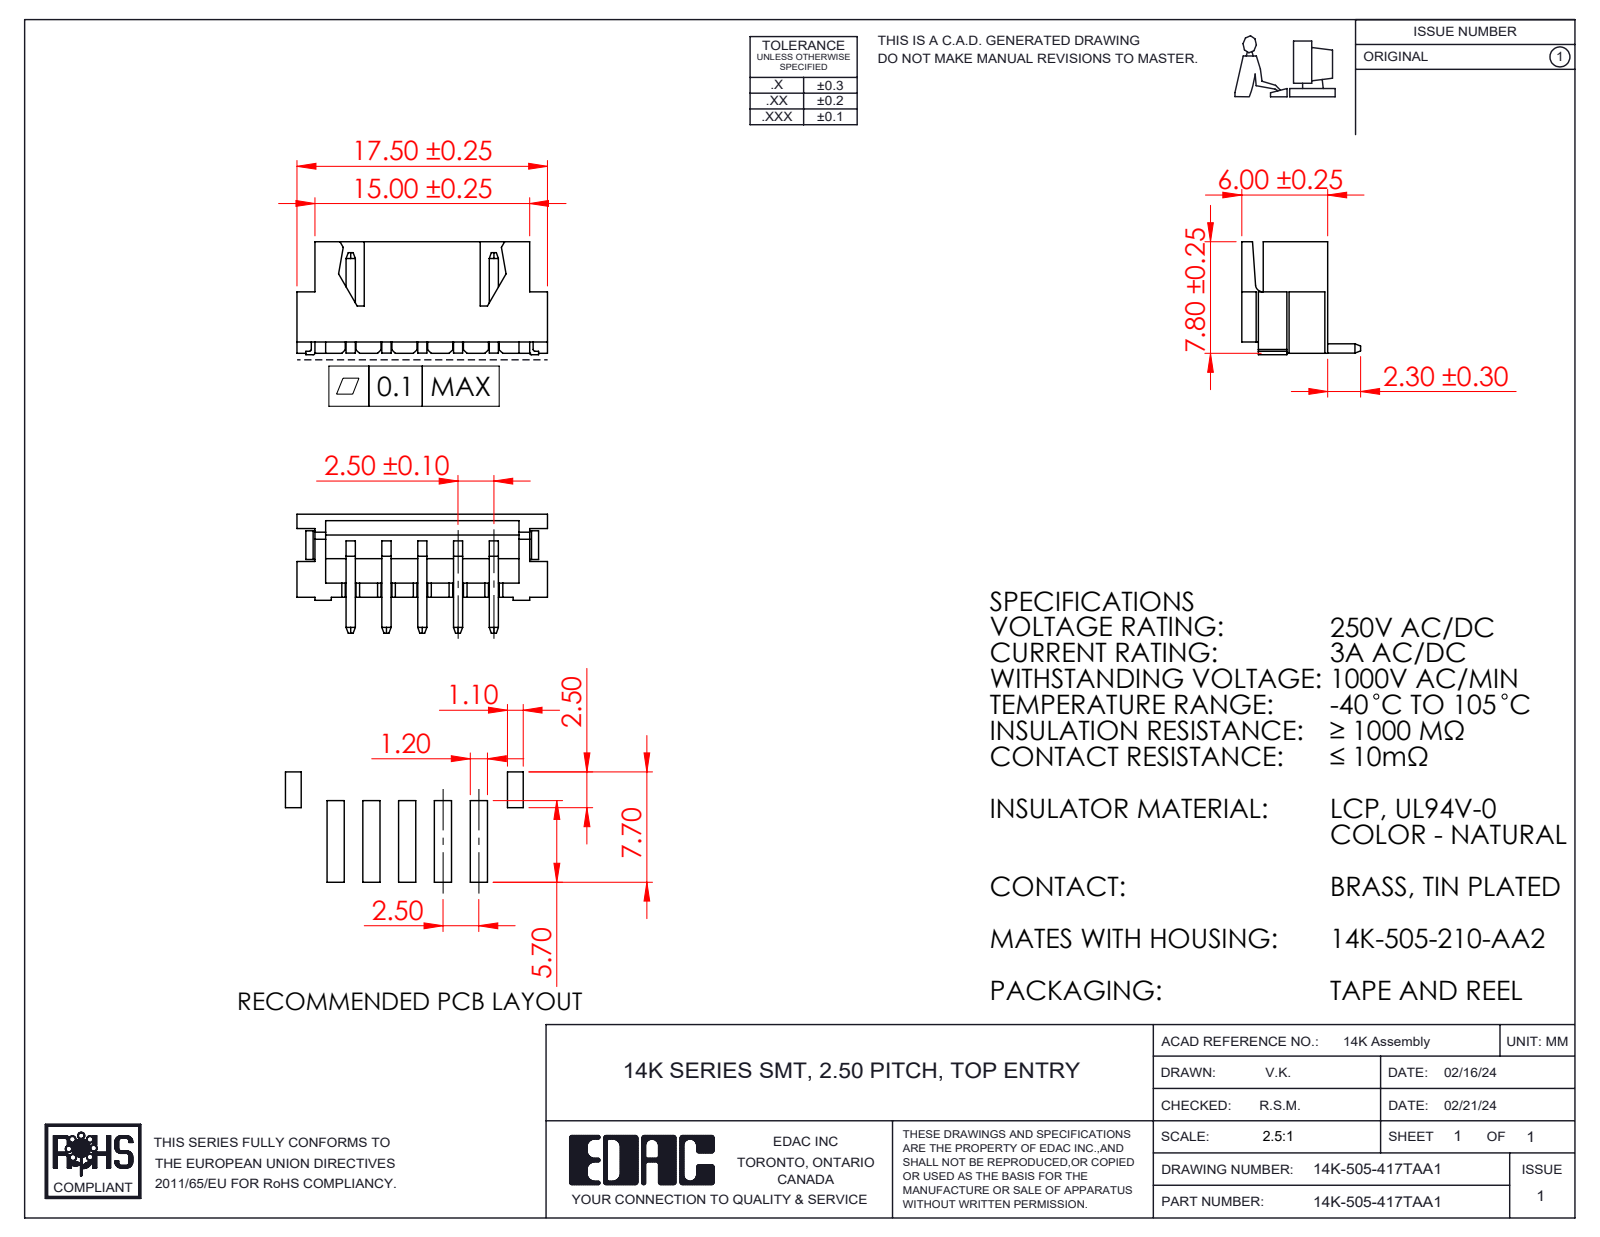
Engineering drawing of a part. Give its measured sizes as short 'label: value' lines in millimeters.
name: 14K-505-418TAA1; 14K Series SMT Top Entry Insulator_505; 14K Series SMT Pin_Top Entry
written by: SolidWorks 2023 (CONFIG_CONTROL_DESIGN)
unit: mm
bodies: 6 solids, 302 faces (276 planar, 26 cylindrical, 0 other)
size: 17.5 × 8.3 × 7.9
volume: 326 mm³; area: 999 mm²
rounds: 10× R0.38, 4× R0.12, 1× R0.43, 1× R0.5, 1× R1.07
face distances: 0.75, 5.8, 5.05, 2.5, 1, 0.64, 1.25, 4.3, 5, 2
